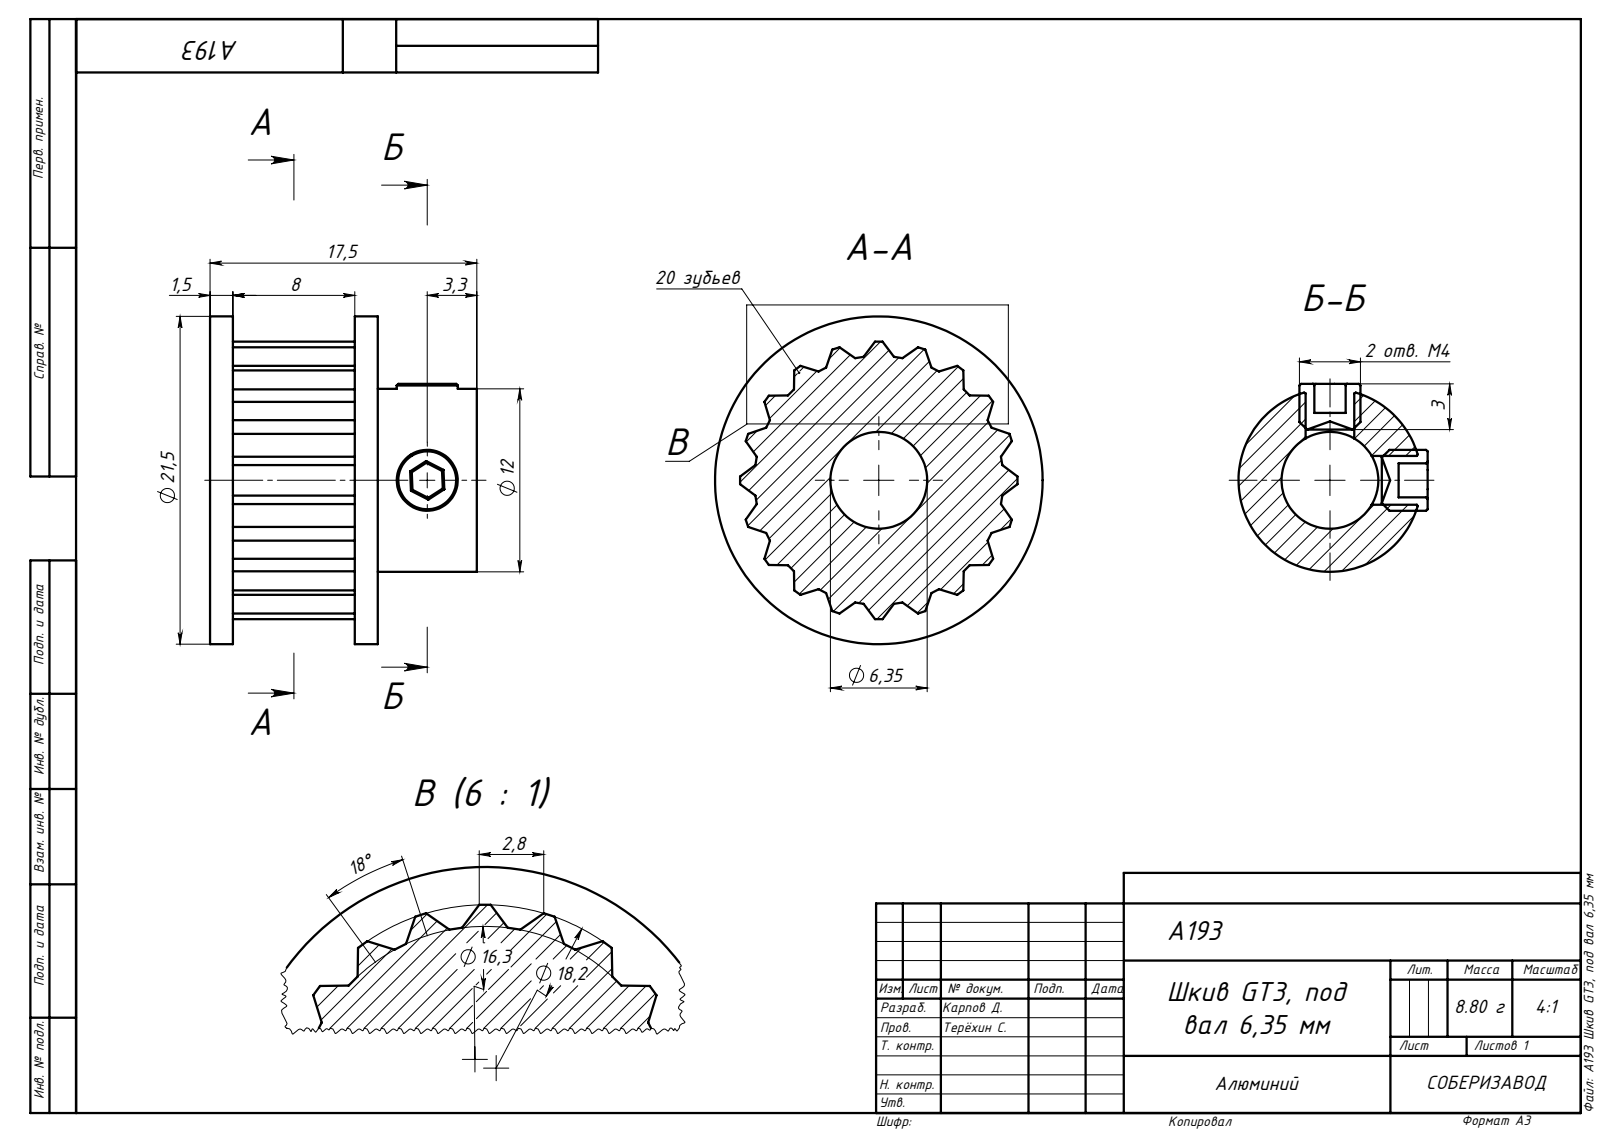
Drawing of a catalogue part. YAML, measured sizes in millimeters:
part_name: "A193 Шкив GT3, под вал 6,35 мм; A193 Шкив GT3, под вал 6,35 мм(подробная модель)"
step_written_by: "SolidWorks 2019 (AUTOMOTIVE_DESIGN)"
units: millimeters
bodies: {solids: 3, faces: 149, planar: 103, cylindrical: 30, other: 16}
overall_size: [21.5, 21.5, 17.5]
volume: 3189
surface_area: 2491
round_holes:
  - {diameter: 3.2, count: 2}
  - {diameter: 6.35, count: 1}
round_bosses_or_shafts:
  - {diameter: 4, count: 2}
  - {diameter: 21.5, count: 1}
  - {diameter: 12, count: 1}
partial_cylinders:
  - {radius: 0.1, count: 12}
face_to_face_distances: [1.5, 9.5, 11, 8, 11.32, 17.5, 16, 6.5, 18.2, 11.31]
